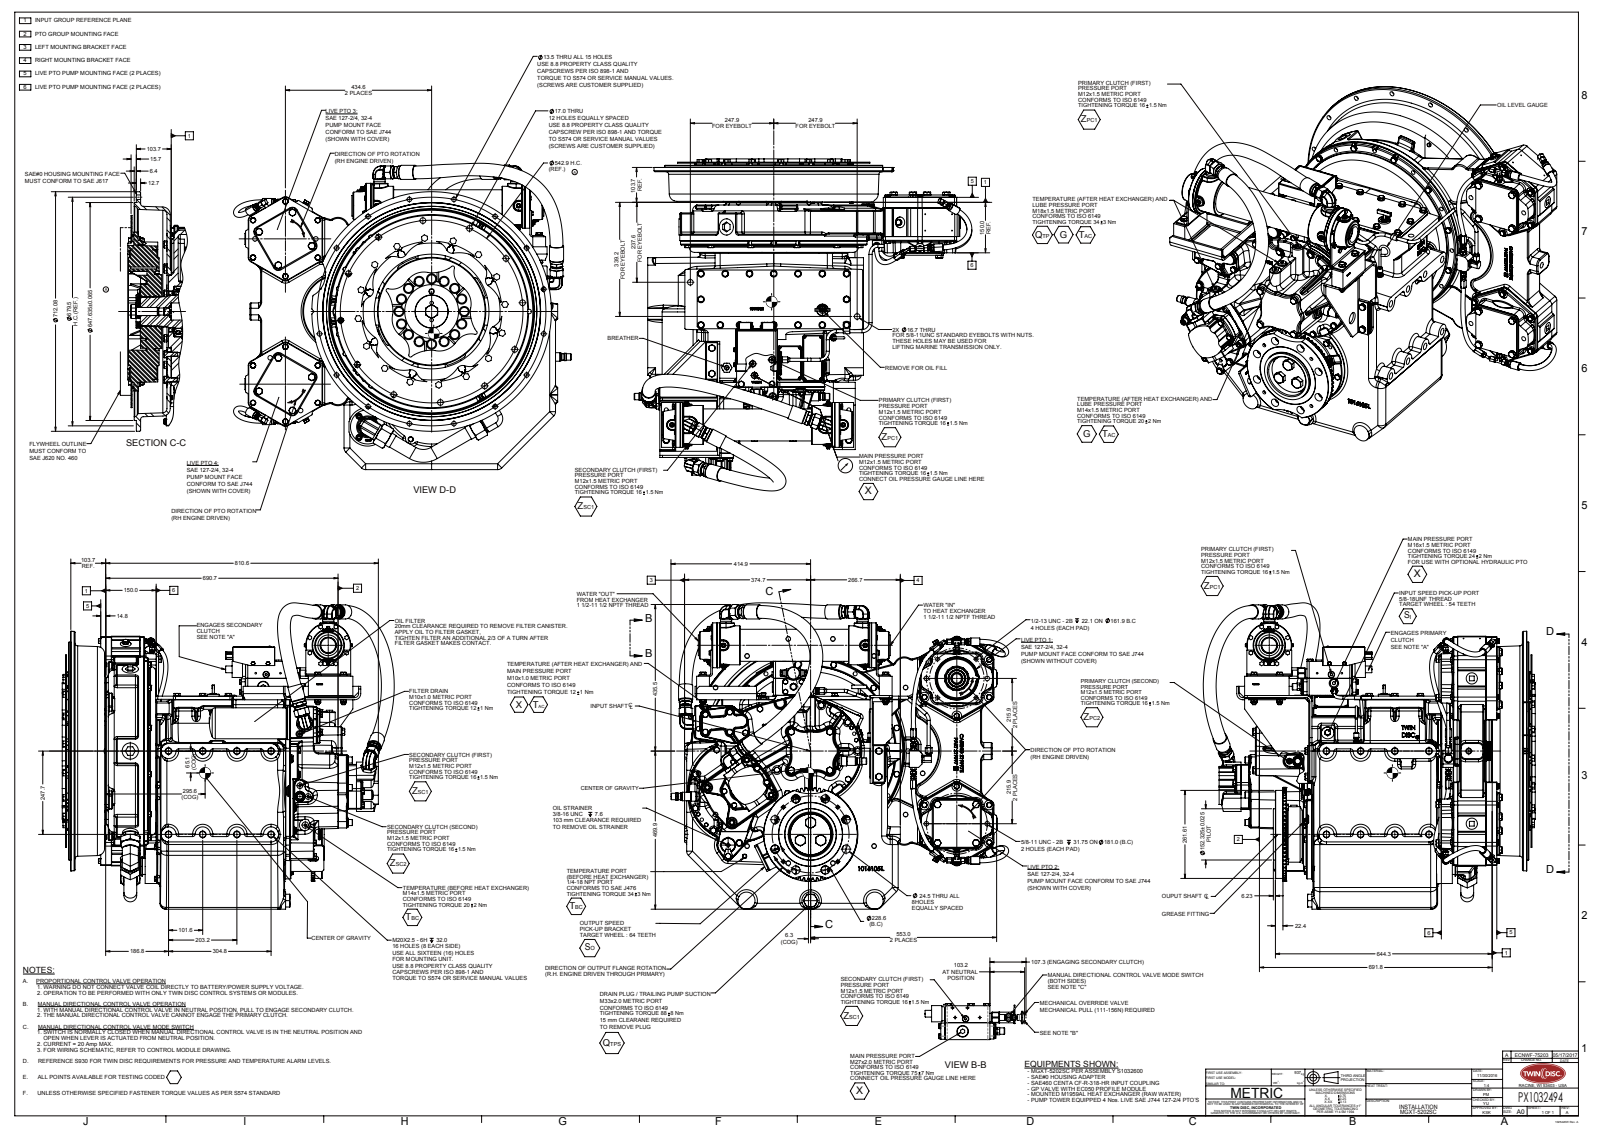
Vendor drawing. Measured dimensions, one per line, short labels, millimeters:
name: PX1032494
written by: SolidWorks 2015 (AUTOMOTIVE_DESIGN)
unit: mm
bodies: 0 solids, 5770 faces (2601 planar, 1427 cylindrical, 1742 other)
size: 1003.8 × 986.8 × 910.5
holes: 16× ⌀13.5, 12× ⌀17, 8× ⌀20, 8× ⌀24.5, 7× ⌀10, 7× ⌀11.9, 4× ⌀13.5, 4× ⌀13.5, 4× ⌀19.1, 3× ⌀9.3, 2× ⌀4.8, 2× ⌀10.3
bosses: 20× ⌀20, 16× ⌀24, 11× ⌀15.7, 8× ⌀81, 7× ⌀9.5, 7× ⌀6.4, 6× ⌀38.1, 6× ⌀30
rounds: 113× R3, 89× R6.4, 77× R46.3, 63× R3, 56× R7.9, 51× R12, 32× R1.5, 32× R17.5
face distances: 551.2, 0.4, 550.8, 560.9, 560.6, 9.7, 6.4, 667.6, 667.2, 116.4
hole spacings: 114.3, 161.6, 44.6, 87.5, 127, 190.1, 211.2, 224.2
